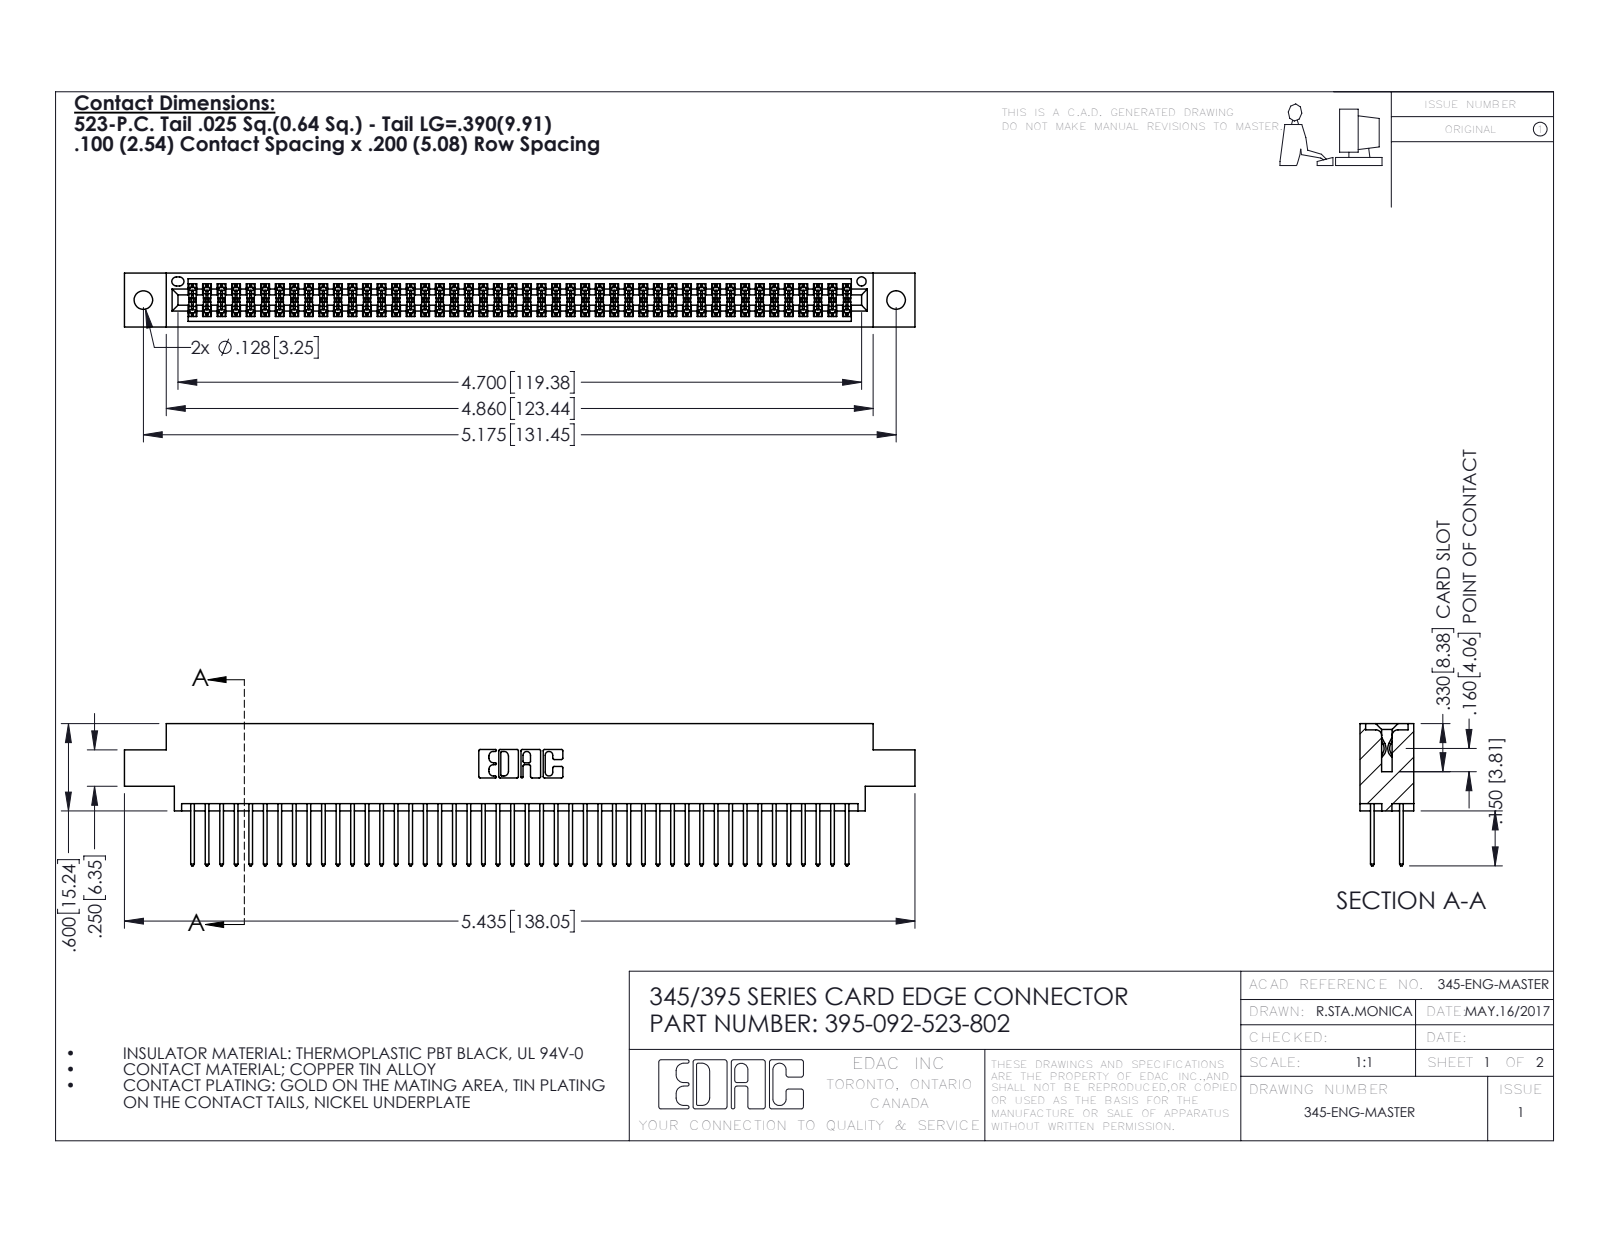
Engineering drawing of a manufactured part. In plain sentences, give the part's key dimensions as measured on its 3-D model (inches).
The part is named "345 Part_0.170 Offset - 0.128 Dia; 345-292-001_345-293-123; 395-092-523-802". Its 3-D file was written by "SolidWorks 2016 (CONFIG_CONTROL_DESIGN)". It is 93 solids with 4730 faces: 3120 planar, 1610 cylindrical and 0 other. Overall it measures 5.435 by 0.977 by 0.37 inches. Its volume is 0.823 cubic inches and its surface area 32.13 square inches. Round holes: 2 of diameter 0.128, 1 of diameter 0.064. Partial cylindrical surfaces (rounded edges, fillets, slot ends): 138 of radius 0.006, 92 of radius 0.01, 22 of radius 0.01, 6 of radius 0.007, 6 of radius 0.031, 3 of radius 0.026, 2 of radius 0.014, 2 of radius 0.019. The main face-to-face distances are 0.298, 0.072, 0.2, 0.098, 0.272, 0.025, 0.37, 0.225, 0.175, 0.149. The hole center spacings are 0.27, 4.939, 5.175.
